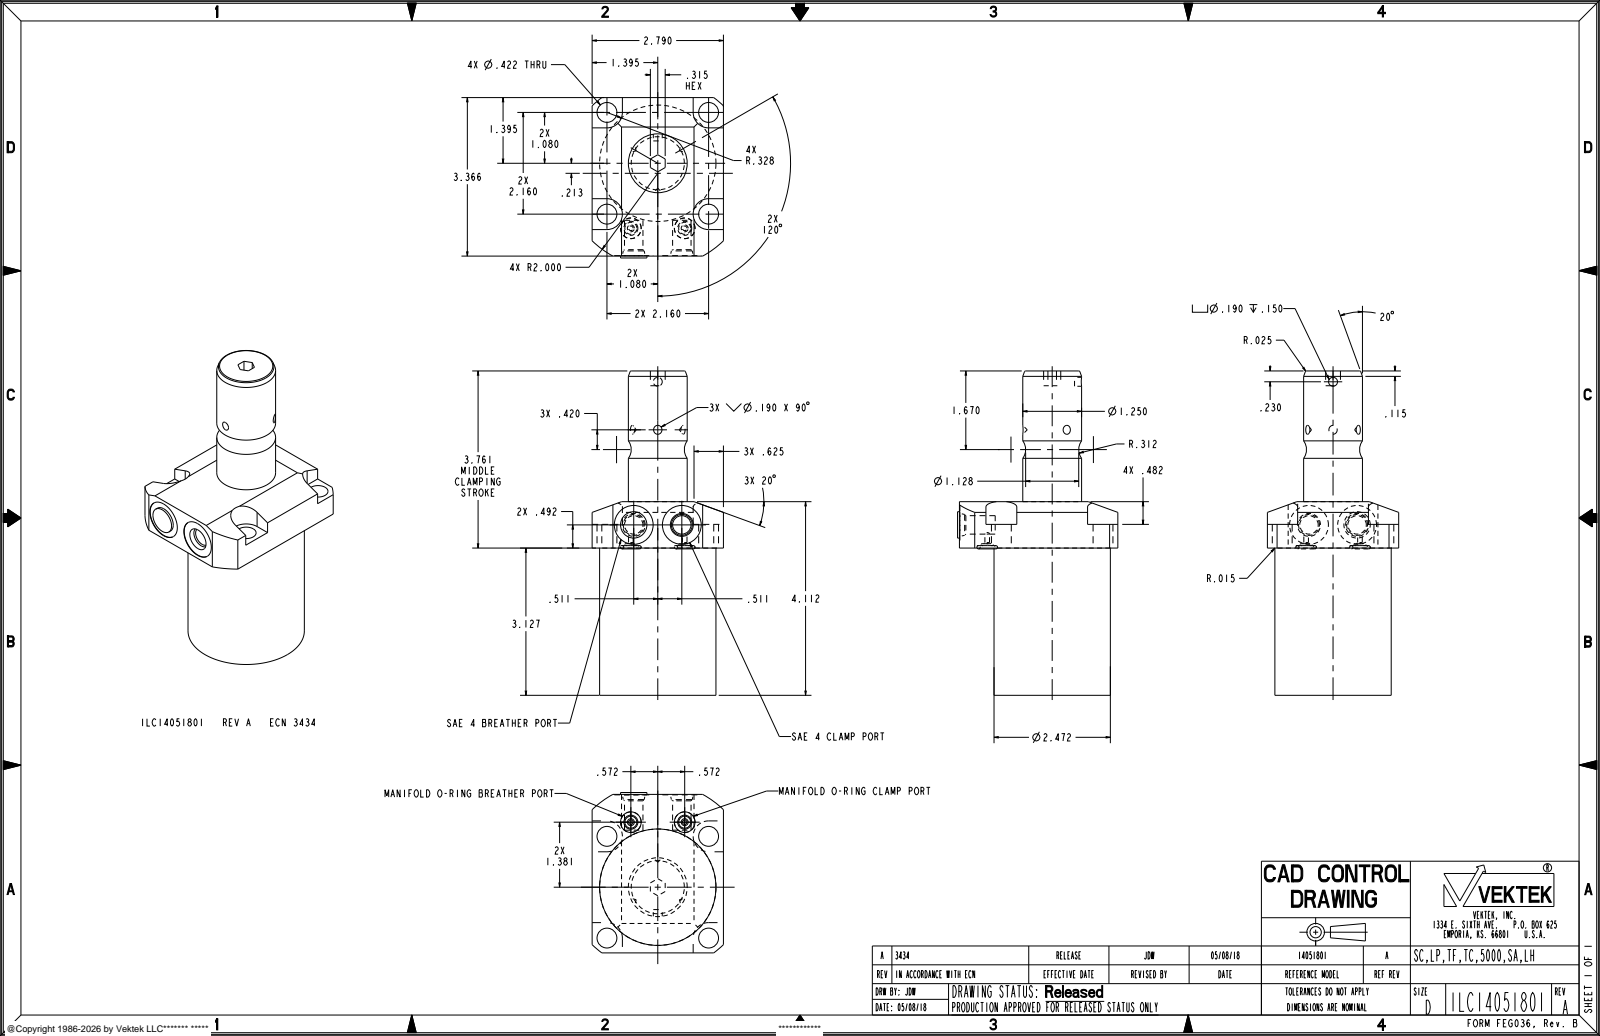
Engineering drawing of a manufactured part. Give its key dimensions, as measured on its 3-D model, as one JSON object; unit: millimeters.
{"part_name": "ILC14051801", "step_written_by": "PRO/ENGINEER BY PARAMETRIC TECHNOLOGY CORPORATION, 2013320 (AUTOMOTIVE_DESIGN)", "units": "millimeters", "bodies": {"solids": 3, "faces": 123, "planar": 43, "cylindrical": 46, "other": 34}, "overall_size": [175, 86.5, 70.9], "volume_mm3": 423000, "surface_area_mm2": 44730, "round_holes": [[10.7, 4], [2.5, 2], [6.5, 2], [10, 2], [11.1, 2], [21, 2], [4.8, 1]], "round_bosses_or_shafts": [[62.8, 1], [31.8, 1], [14.2, 1]], "partial_cylinders_radius": [[8.3, 4], [50.8, 1]], "face_to_face_distances": [79.4, 104.4, 25, 70.9, 92.2, 12.8, 12.2, 175, 95.5, 82.8], "hole_center_spacings": [54.9, 15, 42.6, 63.8, 75.3, 77.6, 78.3, 26]}
